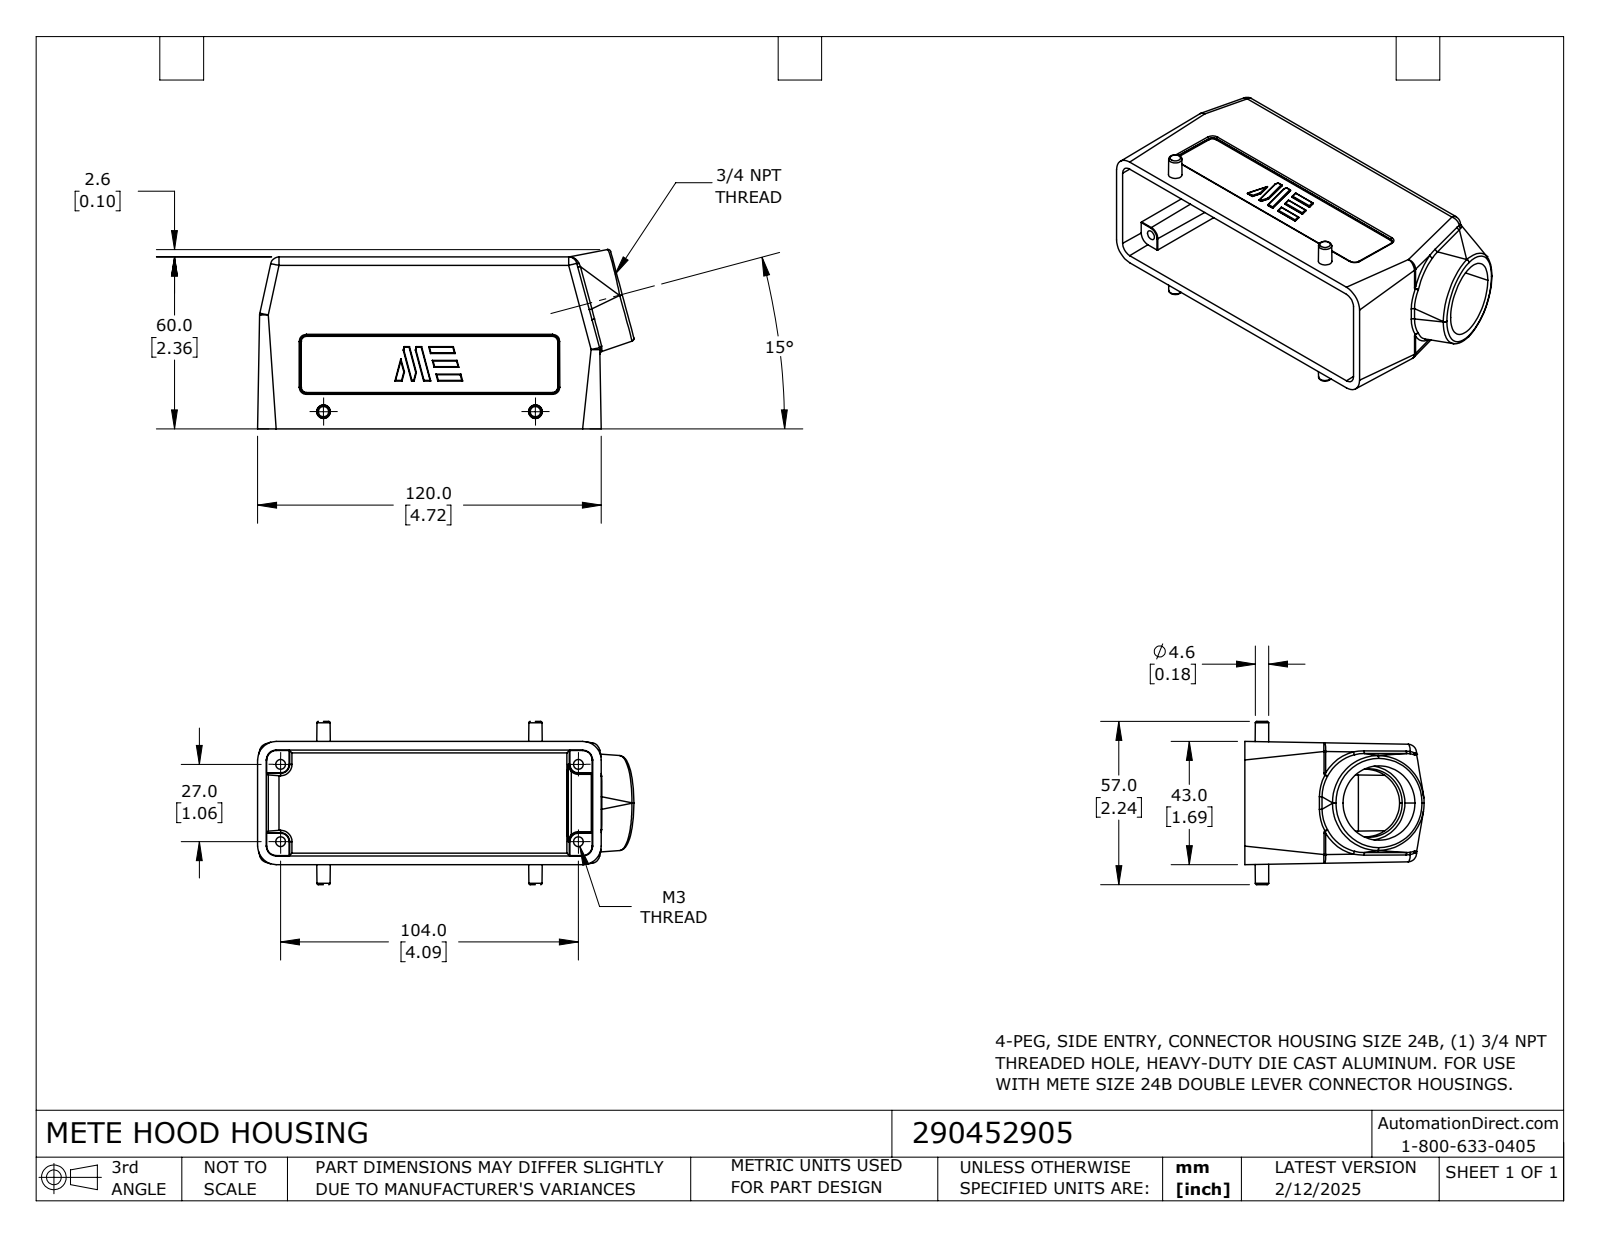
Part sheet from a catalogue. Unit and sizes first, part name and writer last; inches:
Units: inches
Overall size (bounding box): 5.173 × 2.466 × 2.244
Round holes (diameter × count): ⌀0.134 ×4
Partial cylindrical surfaces — rounded edges, fillets, slot ends (radius × count): R0.008 ×46, R0.02 ×8, R0.079 ×8, R0.118 ×8, R0.039 ×4, R0.098 ×2, R0.512 ×2
Main face-to-face distances: 0.118, 0.087, 0.031, 0.433, 0.315, 2.244, 2.362, 0.402, 0.354, 1.89
Hole centre spacings: 1.063, 4.094, 4.23
Volume: 4.66 in³ · Surface area: 71.73 in²
Bodies: 1 solid, 316 faces (117 planar, 111 cylindrical, 88 other)
Part name (STEP PRODUCT): 290452905
STEP written by: SolidWorks 2024 (CONFIG_CONTROL_DESIGN)
